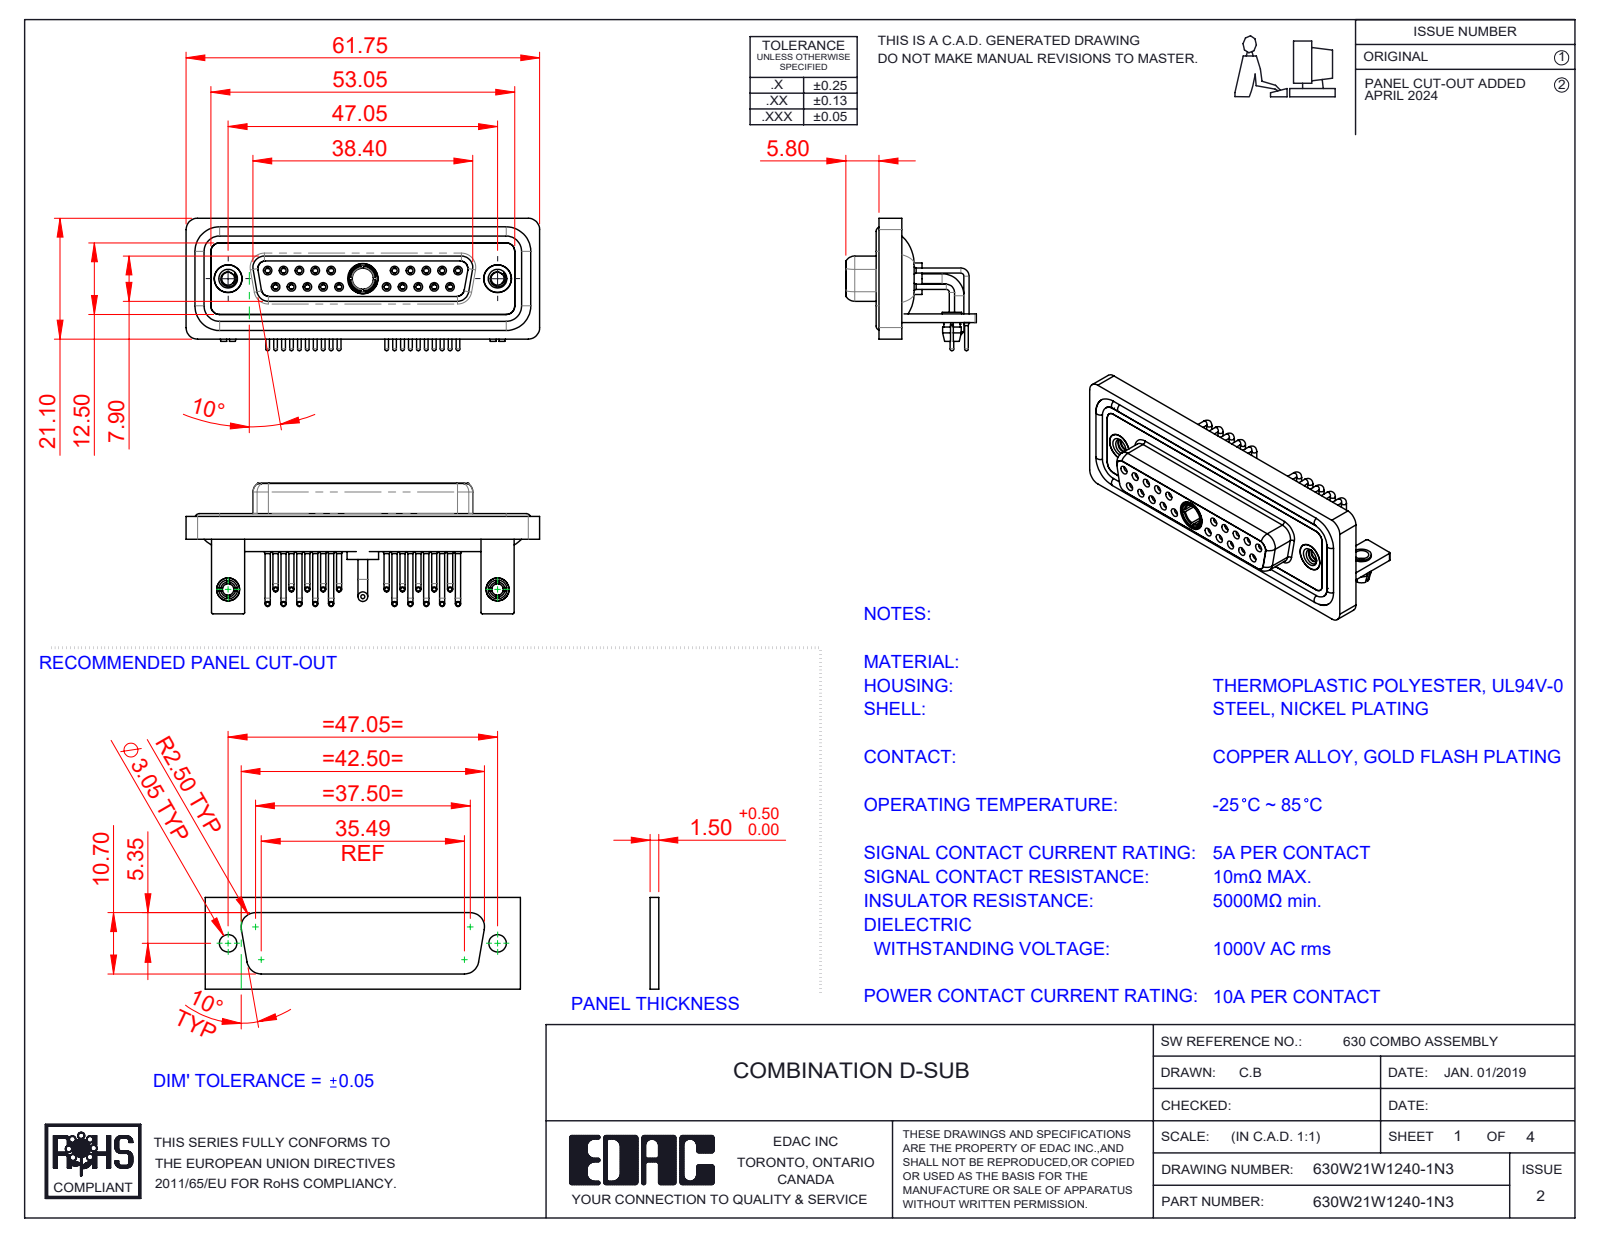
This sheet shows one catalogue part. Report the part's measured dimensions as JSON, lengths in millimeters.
{"part_name": "630Combo Contact Row 1_50 Contacts; 630Combo Board Lock_50 Contacts; 630Combo Waterproof Housing_25 Contacts; 630Combo Shell Rear_25 Contacts (+7 more)", "step_written_by": "SolidWorks 2023 (CONFIG_CONTROL_DESIGN)", "units": "millimeters", "bodies": {"solids": 33, "faces": 1664, "planar": 502, "cylindrical": 729, "other": 433}, "overall_size": [61.75, 23.12, 22.8], "volume_mm3": 8851, "surface_area_mm2": 15675, "round_holes": [[2, 22], [0.9, 20], [1.1, 20], [1.5, 20], [1.6, 10], [1.7, 10], [4.85, 3], [2.26, 2], [2.5, 2], [3.2, 2], [4, 2], [4.05, 2]], "round_bosses_or_shafts": [[0.9, 20], [0.65, 20], [1.6, 14], [4.95, 2], [4.8, 2], [4, 2], [3.4, 2], [3.3, 2]], "partial_cylinders_radius": [[2, 19], [1.5, 18], [0.25, 16], [1.35, 8], [1.6, 8], [0.5, 5], [0.6, 4], [0.65, 4]], "face_to_face_distances": [0.4, 1.8, 2.9, 3.7, 1.5, 4.1, 1.1, 1.4, 1.6, 2.5], "hole_center_spacings": [3.16, 2.77, 5.54, 8.31, 5.04, 19.39, 20.97, 22.16]}
